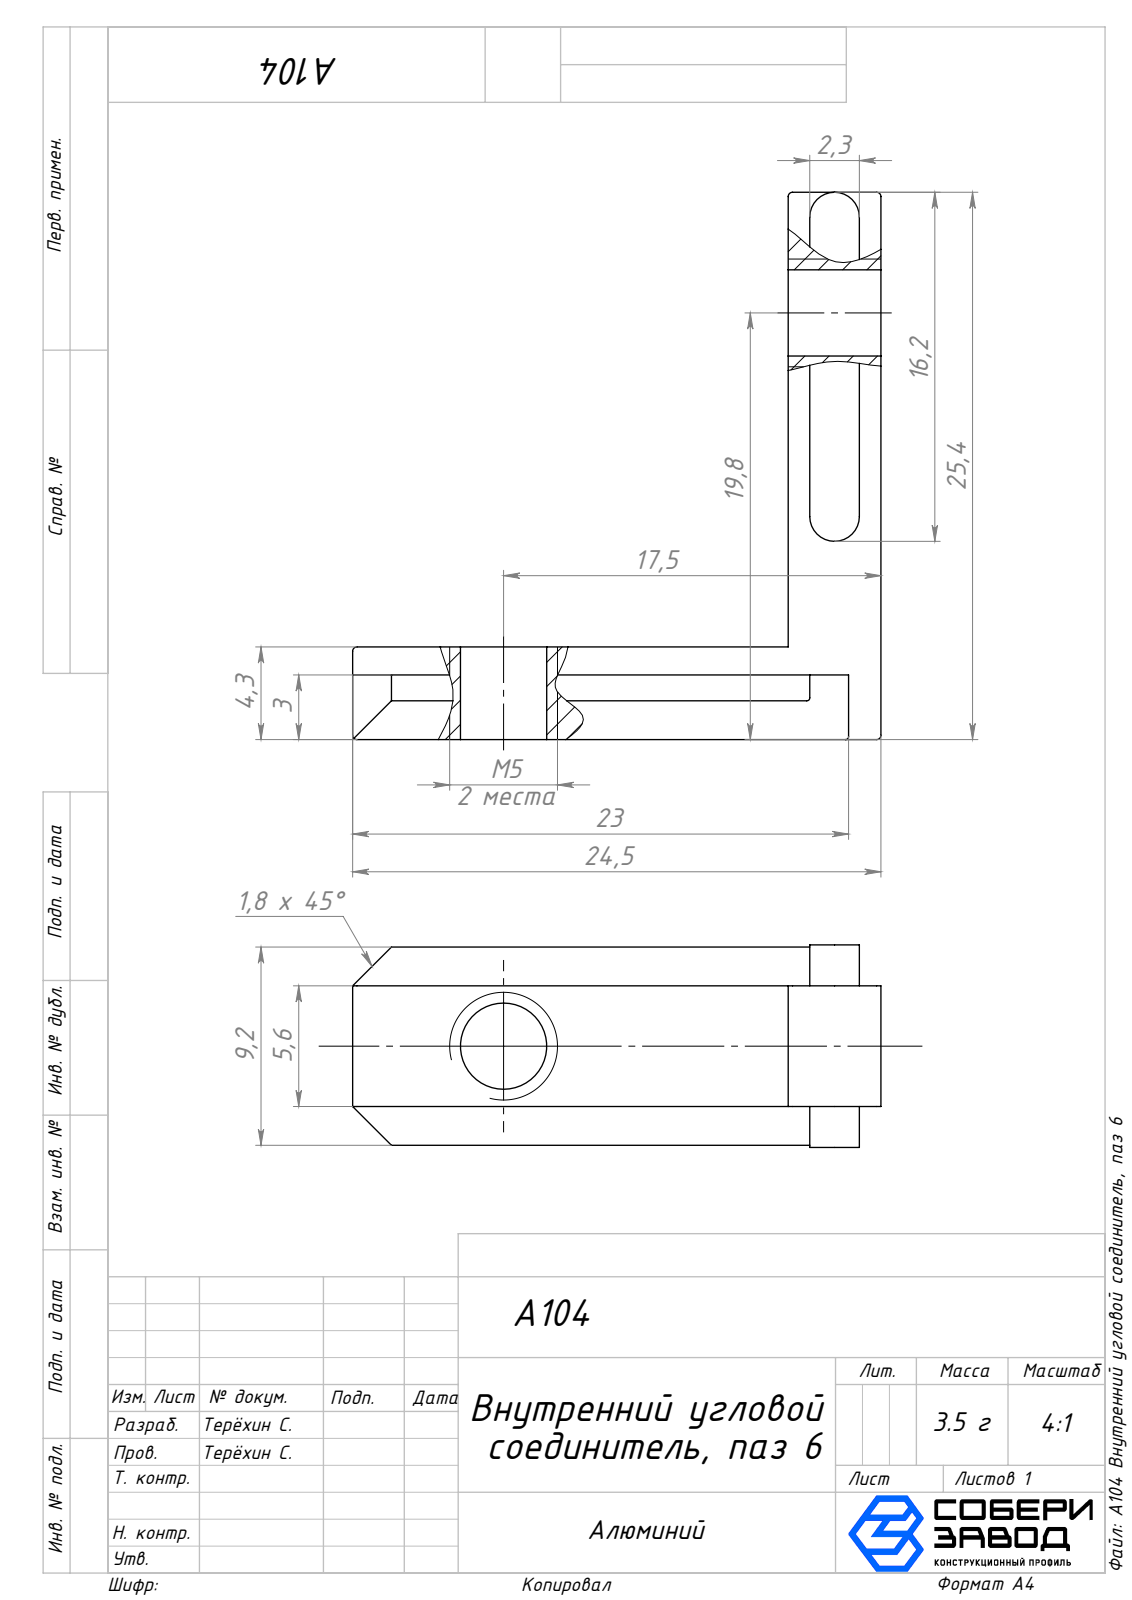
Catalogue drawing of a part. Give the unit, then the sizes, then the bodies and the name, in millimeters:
Units: millimetres
Overall size (bounding box): 25.4 × 24.5 × 9.4
Round holes (diameter × count): ⌀4 ×2
Partial cylindrical surfaces — rounded edges, fillets, slot ends (radius × count): R0.2 ×7, R1.15 ×2
Main face-to-face distances: 4.3, 1, 3.3, 5.6, 3, 1.3, 1.9, 7.5, 2.3, 9.3
Volume: 1 289 mm³ · Surface area: 1 254 mm²
Bodies: 1 solid, 43 faces (24 planar, 19 cylindrical, 0 other)
Part name (STEP PRODUCT): A104 Внутренний угловой соединитель, паз 6_00; A104 Внутренний угловой соединитель, паз 6
STEP written by: SolidWorks 2026 (CONFIG_CONTROL_DESIGN)
